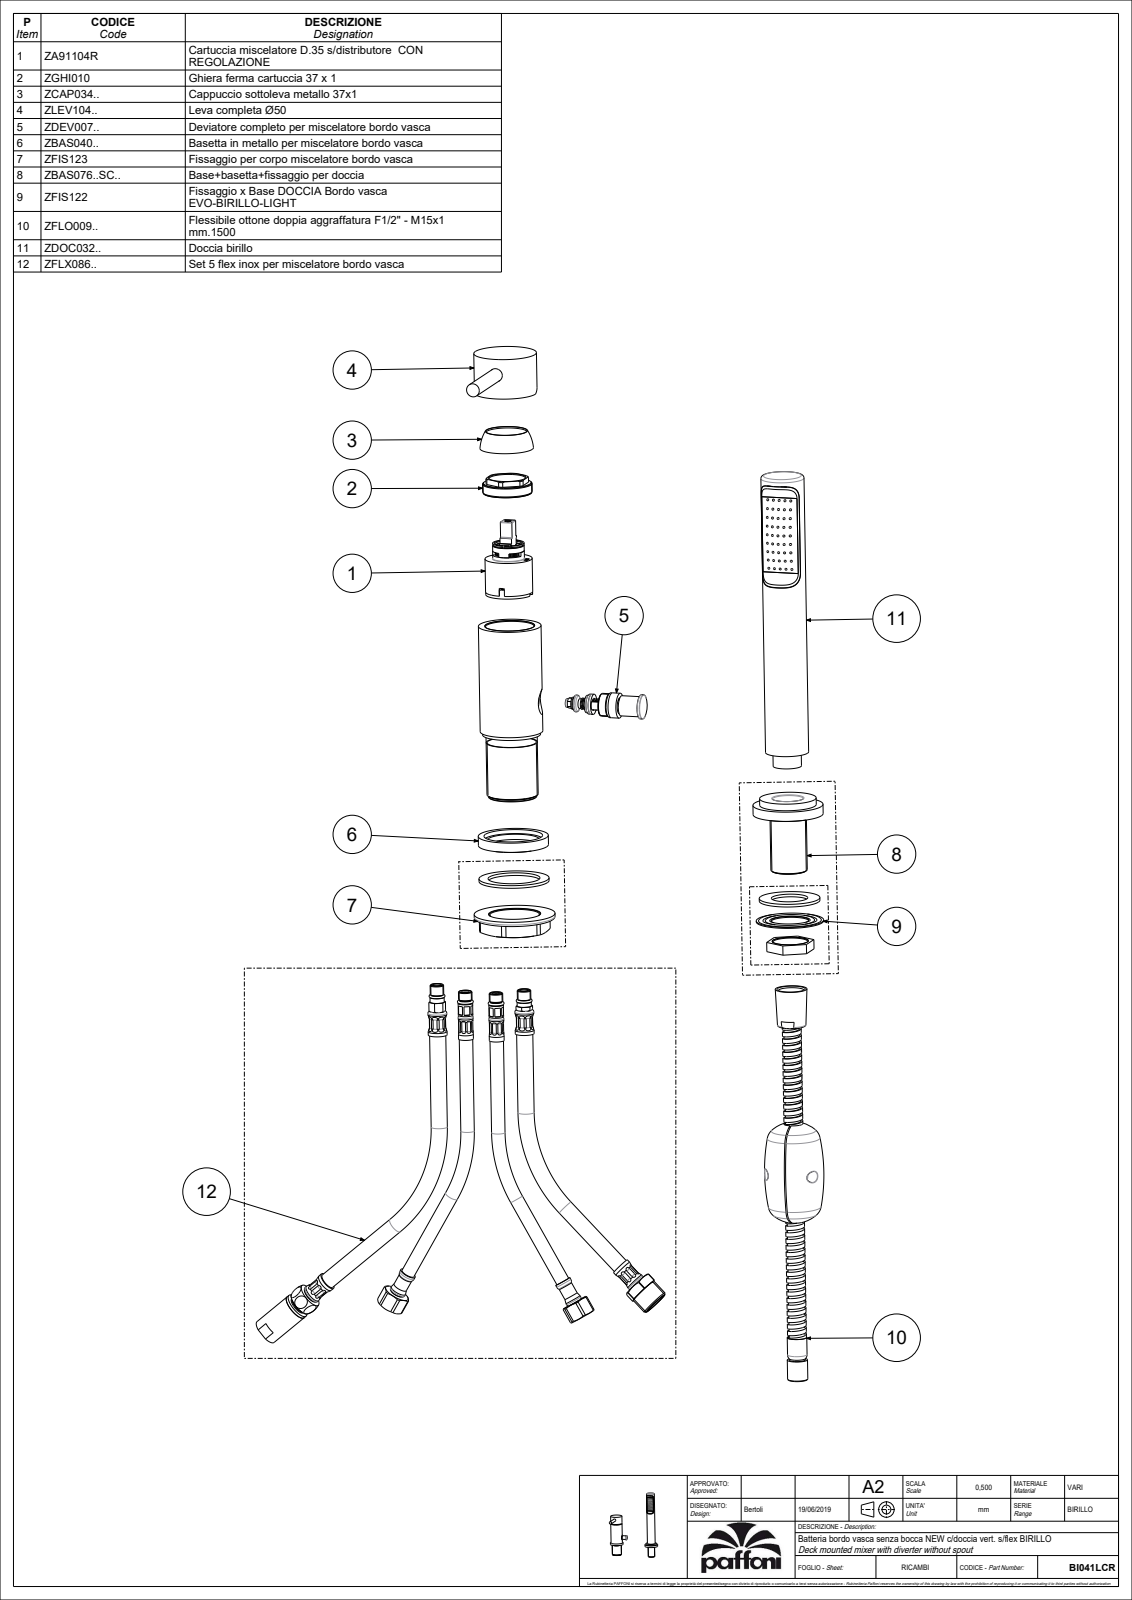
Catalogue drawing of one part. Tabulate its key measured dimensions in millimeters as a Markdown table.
| quantity | value |
| --- | --- |
| part name | BI041LCR |
| STEP written by | CREO PARAMETRIC BY PTC INC, 2020044 (CONFIG_CONTROL_DESIGN) |
| units | millimeters |
| bodies | 3 solids, 1216 faces (626 planar, 403 cylindrical, 187 other) |
| overall size | 221.5 × 202 × 103.75 |
| volume | 226 272 mm³ |
| surface area | 112 592 mm² |
| round holes (diameter × count) | 1.5 × 45, 7 × 6, 4 × 2, 10 × 2, 49.2 × 2, 3.1 × 1, 3.3 × 1, 4.2 × 1, 4.3 × 1, 4.5 × 1, 5 × 1, 6 × 1 |
| round bosses / shafts (diameter × count) | 52 × 2, 44.2 × 2, 46.5 × 1, 42 × 1, 38 × 1, 35 × 1, 34.8 × 1, 32.2 × 1 |
| partial cylindrical surfaces (radius × count) | 0.5 × 27, 0.15 × 11, 0.3 × 4, 1 × 2, 7.8 × 2, 9.8 × 2, 10 × 2, 3.9 × 1 |
| main face-to-face distances | 10, 5, 0.5, 2, 219.5, 5.5, 1.5, 79.5, 4.5, 6.5 |
| hole center spacings | 7.91, 13.76, 20.01, 6.5, 13, 26.39, 4.5, 19.5 |
